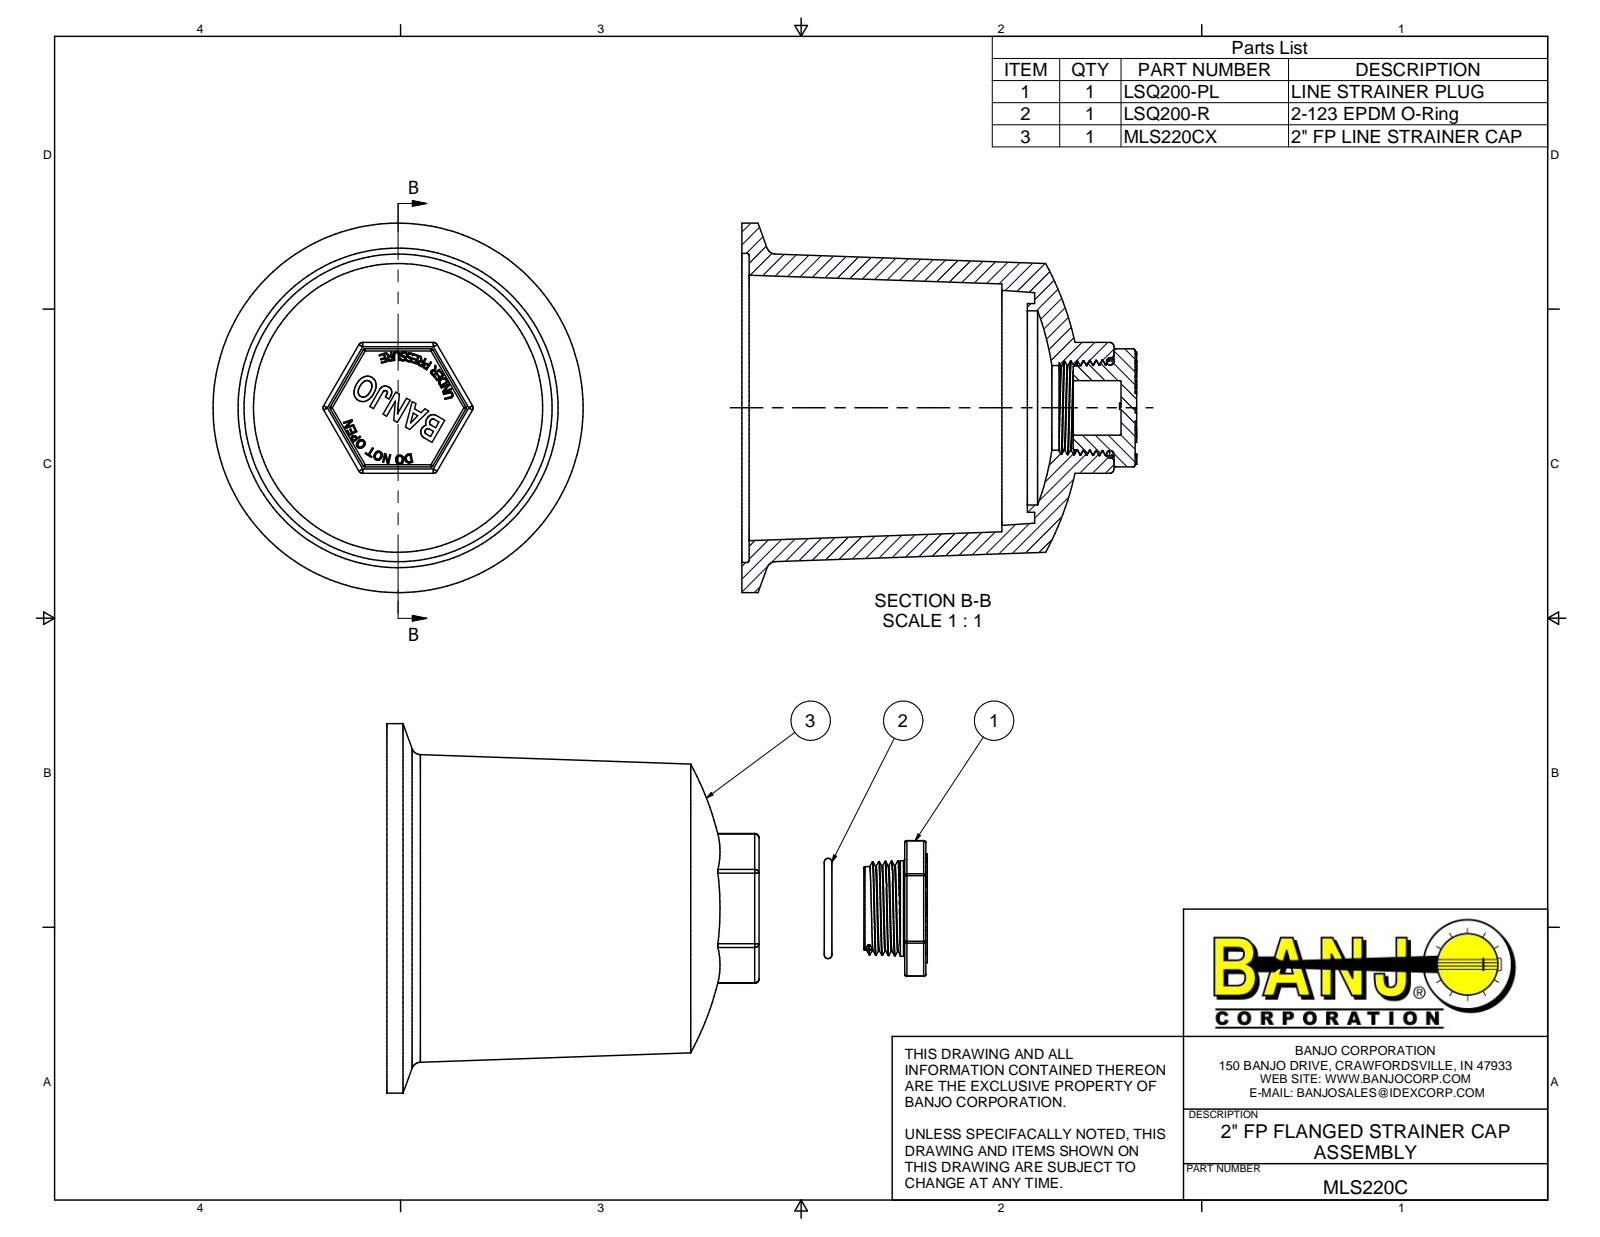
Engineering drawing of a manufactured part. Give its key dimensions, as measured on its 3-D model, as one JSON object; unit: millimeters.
{"part_name": "MLS220CX; LSQ200-R; LSQ200-PL; MLS220C", "step_written_by": "Autodesk Inventor 2016 (AUTOMOTIVE_DESIGN)", "units": "millimeters", "bodies": {"solids": 2, "faces": 552, "planar": 281, "cylindrical": 38, "other": 233}, "overall_size": [137.67, 129.03, 129.03], "volume_mm3": 345527, "surface_area_mm2": 100492, "round_holes": [[19.05, 1], [29.59, 1], [67.82, 1], [107.95, 1]], "round_bosses_or_shafts": [[129.03, 1], [72.9, 1], [33.4, 1]], "partial_cylinders_radius": [[0.76, 18], [1.52, 12], [9.98, 1]], "face_to_face_distances": [2.54, 99.56, 134.62, 137.16, 7.37, 127.25, 129.79, 35.06, 27.69, 102.1]}
